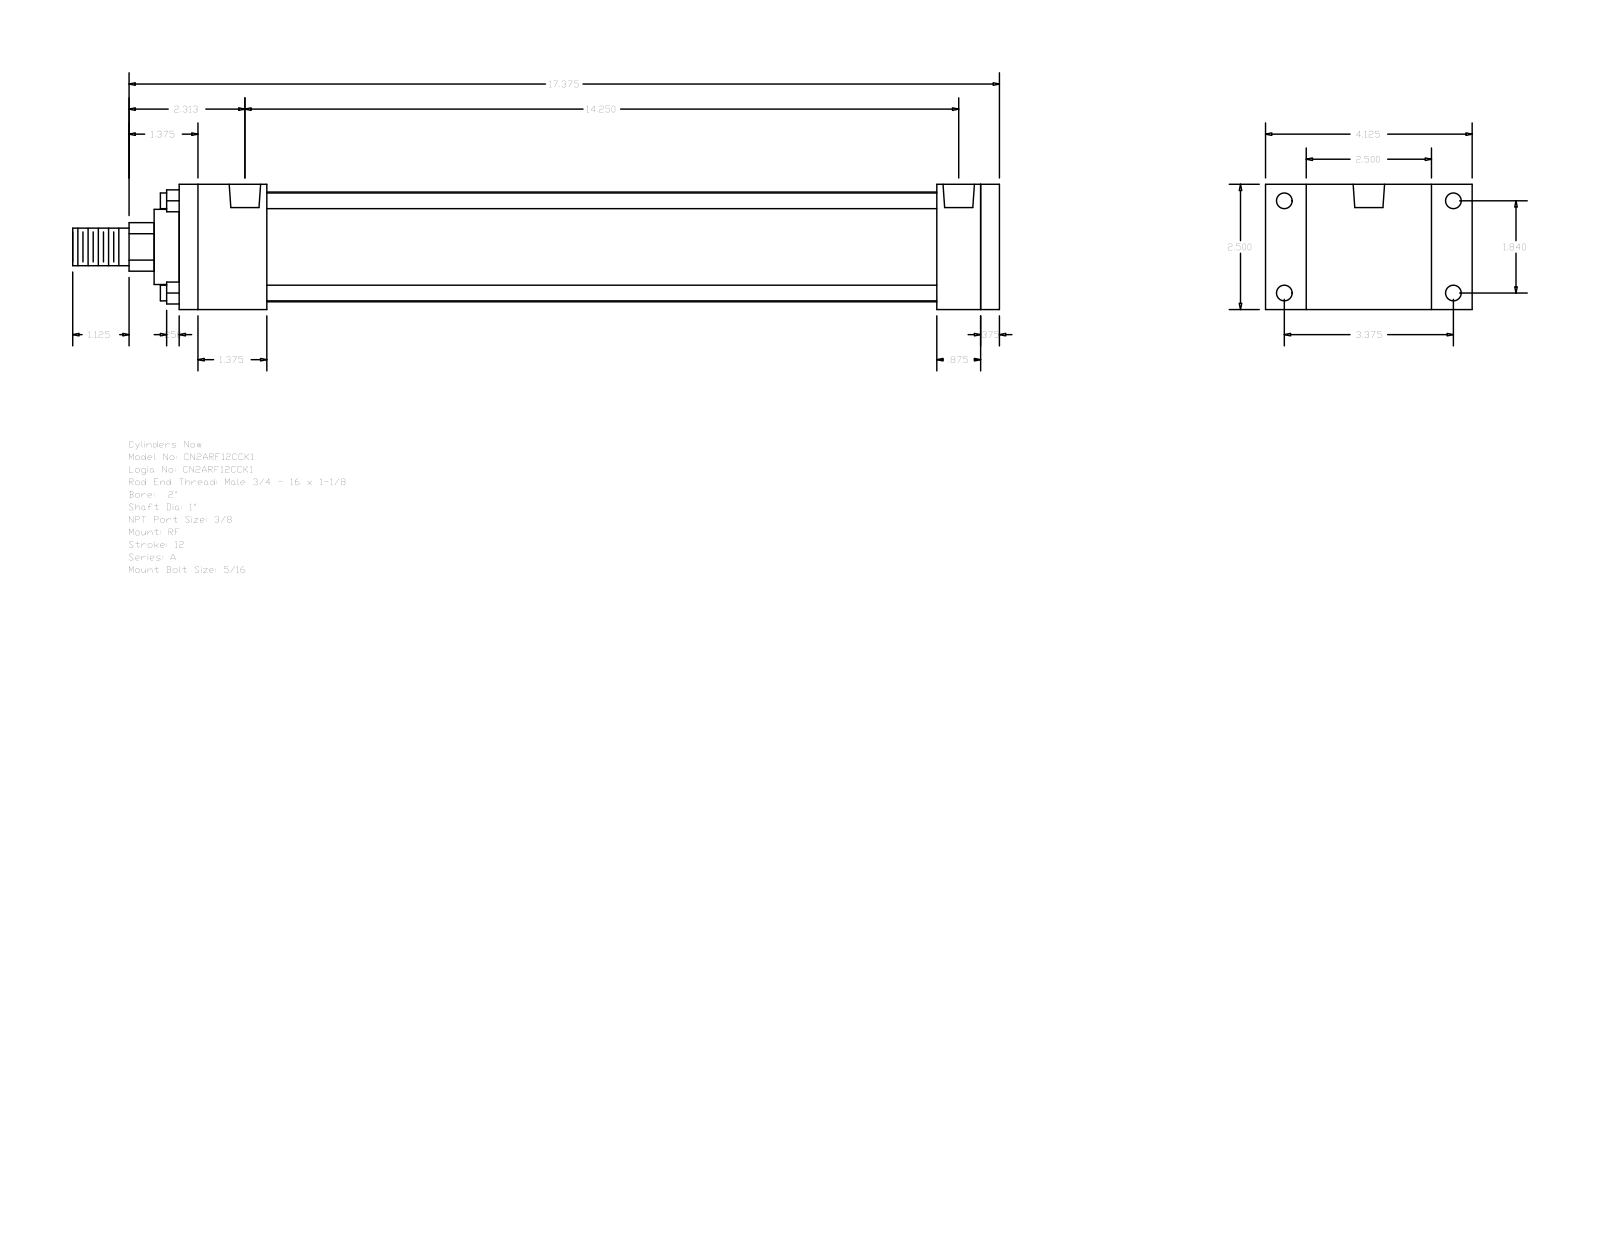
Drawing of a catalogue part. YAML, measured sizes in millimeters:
part_name: "A_RF__0200_1"
step_written_by: "GSSL Pune (CONFIG_CONTROL_DESIGN)"
units: millimeters
bodies: {solids: 0, faces: 92, planar: 64, cylindrical: 28, other: 0}
overall_size: [469.9, 104.78, 63.5]
round_holes:
  - {diameter: 5.56, count: 4}
  - {diameter: 7.94, count: 4}
  - {diameter: 15.93, count: 2}
round_bosses_or_shafts:
  - {diameter: 7.94, count: 4}
  - {diameter: 55.63, count: 1}
  - {diameter: 38.1, count: 1}
  - {diameter: 25.4, count: 1}
  - {diameter: 19.05, count: 1}
partial_cylinders:
  - {radius: 12.29, count: 1}
face_to_face_distances: [63.5, 9.52, 415.92, 406.4, 44.45, 20.64, 361.95, 371.47, 384.17, 339.72]
hole_center_spacings: [46.74, 85.72, 97.63, 356.38, 1.59, 3.98, 357.97, 360.36]
